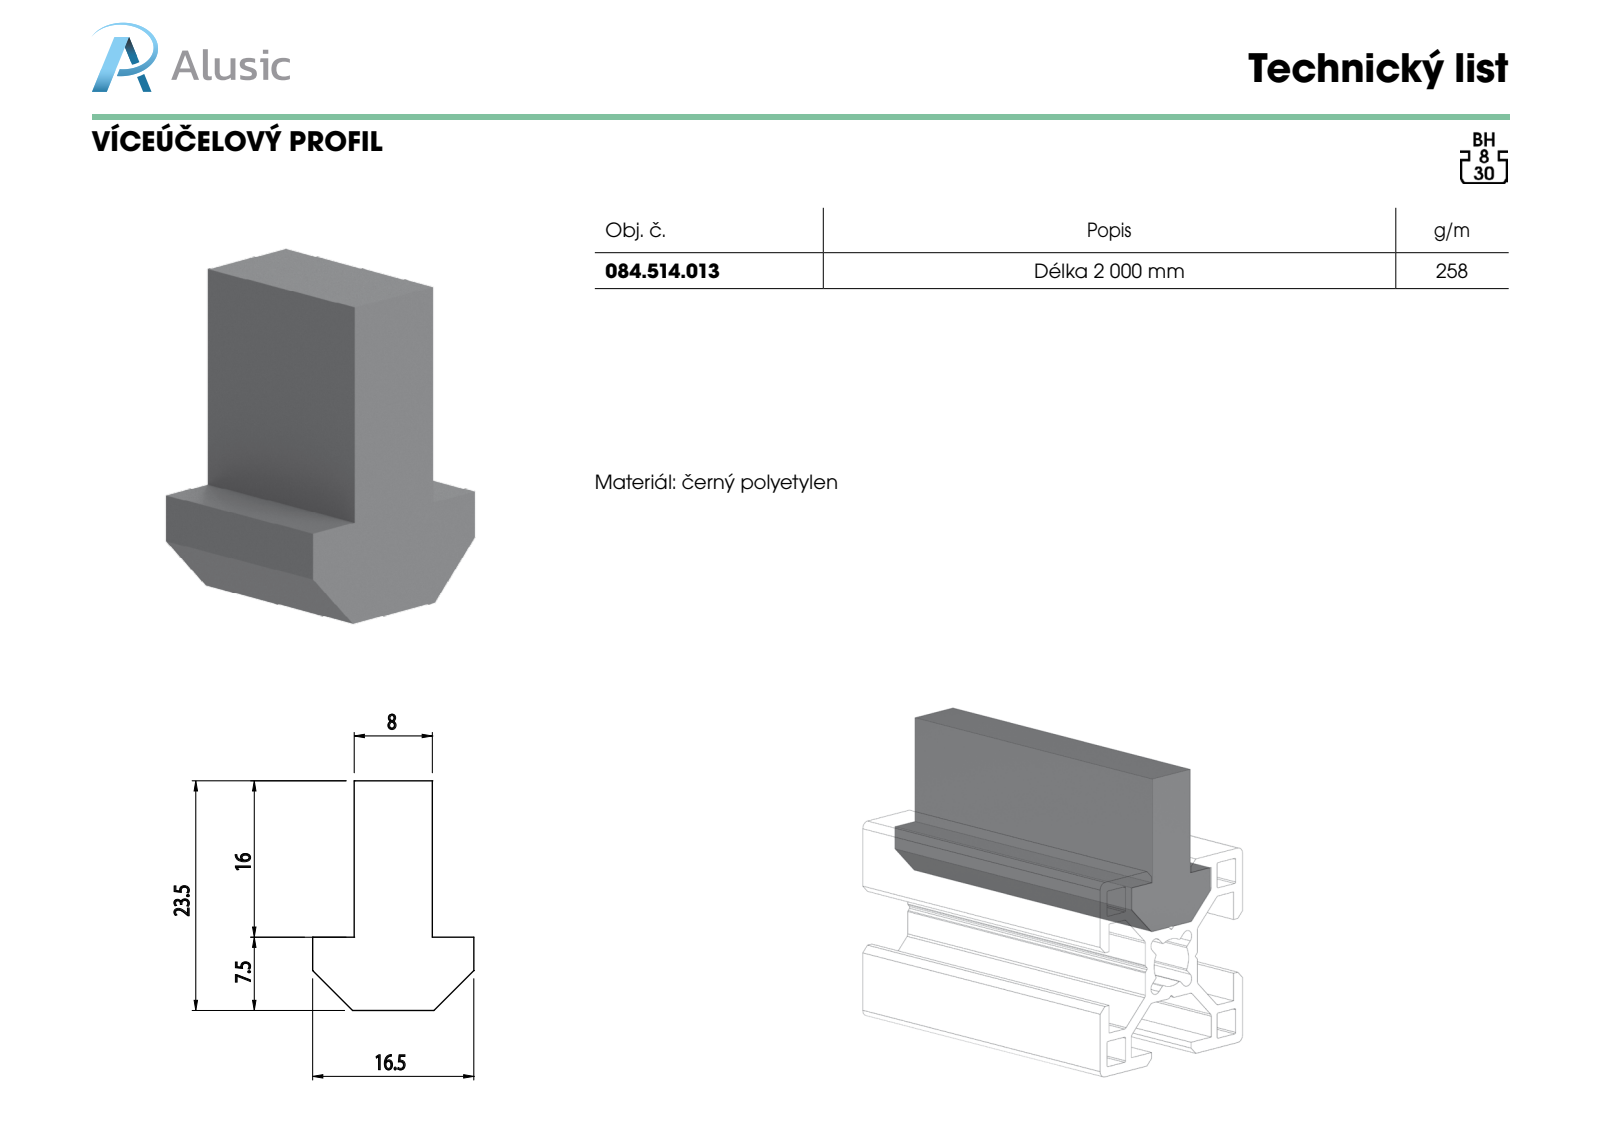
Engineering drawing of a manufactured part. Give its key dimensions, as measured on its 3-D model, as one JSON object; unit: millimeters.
{"part_name": "084.514.013", "step_written_by": "SolidWorks 2012 (CONFIG_CONTROL_DESIGN)", "units": "millimeters", "bodies": {"solids": 1, "faces": 12, "planar": 12, "cylindrical": 0, "other": 0}, "overall_size": [100, 23.5, 16.5], "volume_mm3": 23506, "surface_area_mm2": 7992, "face_to_face_distances": [8, 7.5, 23.5, 16, 4.25, 12.25, 16.5, 100]}
